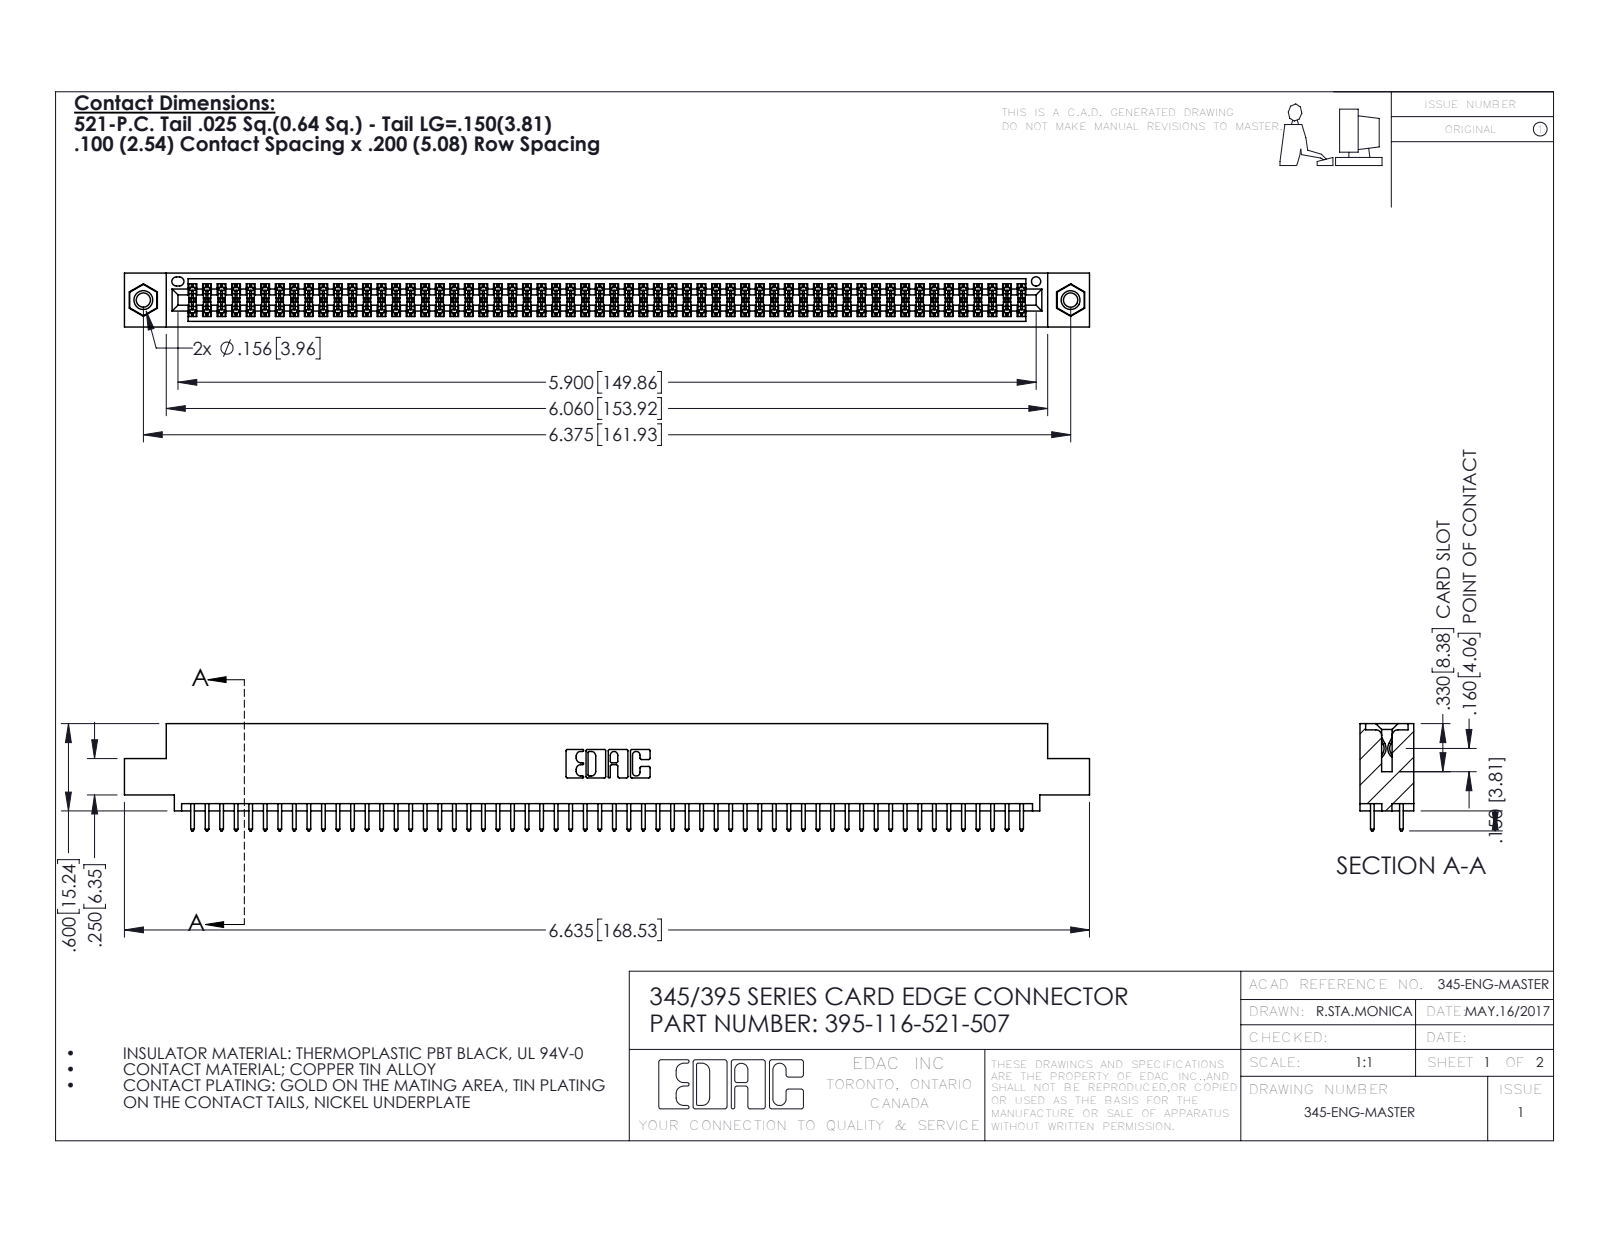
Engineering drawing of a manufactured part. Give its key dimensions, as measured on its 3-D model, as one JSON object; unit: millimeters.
{"part_name": "345 Part_0.110 Offset - 0.156 Dia-TI; 345-250-001_345-250-005-103; 395-116-521-507; 345-292-001_345-293-121", "step_written_by": "SolidWorks 2016 (CONFIG_CONTROL_DESIGN)", "units": "millimeters", "bodies": {"solids": 119, "faces": 5990, "planar": 3944, "cylindrical": 2030, "other": 16}, "overall_size": [168.5, 18.7, 9.4], "volume_mm3": 16390, "surface_area_mm2": 24340, "round_holes": [[2.5, 2], [3.2, 2], [4, 2], [1.6, 1]], "round_bosses_or_shafts": [[3.9, 2]], "partial_cylinders_radius": [[0.2, 174], [0.3, 116], [0.3, 22], [0.2, 6], [0.8, 6], [0.7, 3], [0.4, 2], [0.5, 2]], "face_to_face_distances": [1.8, 7.6, 5.1, 2.5, 6.9, 0.6, 9.4, 5.7, 4.4, 3.8], "hole_center_spacings": [6.9, 155.9, 161.9]}
